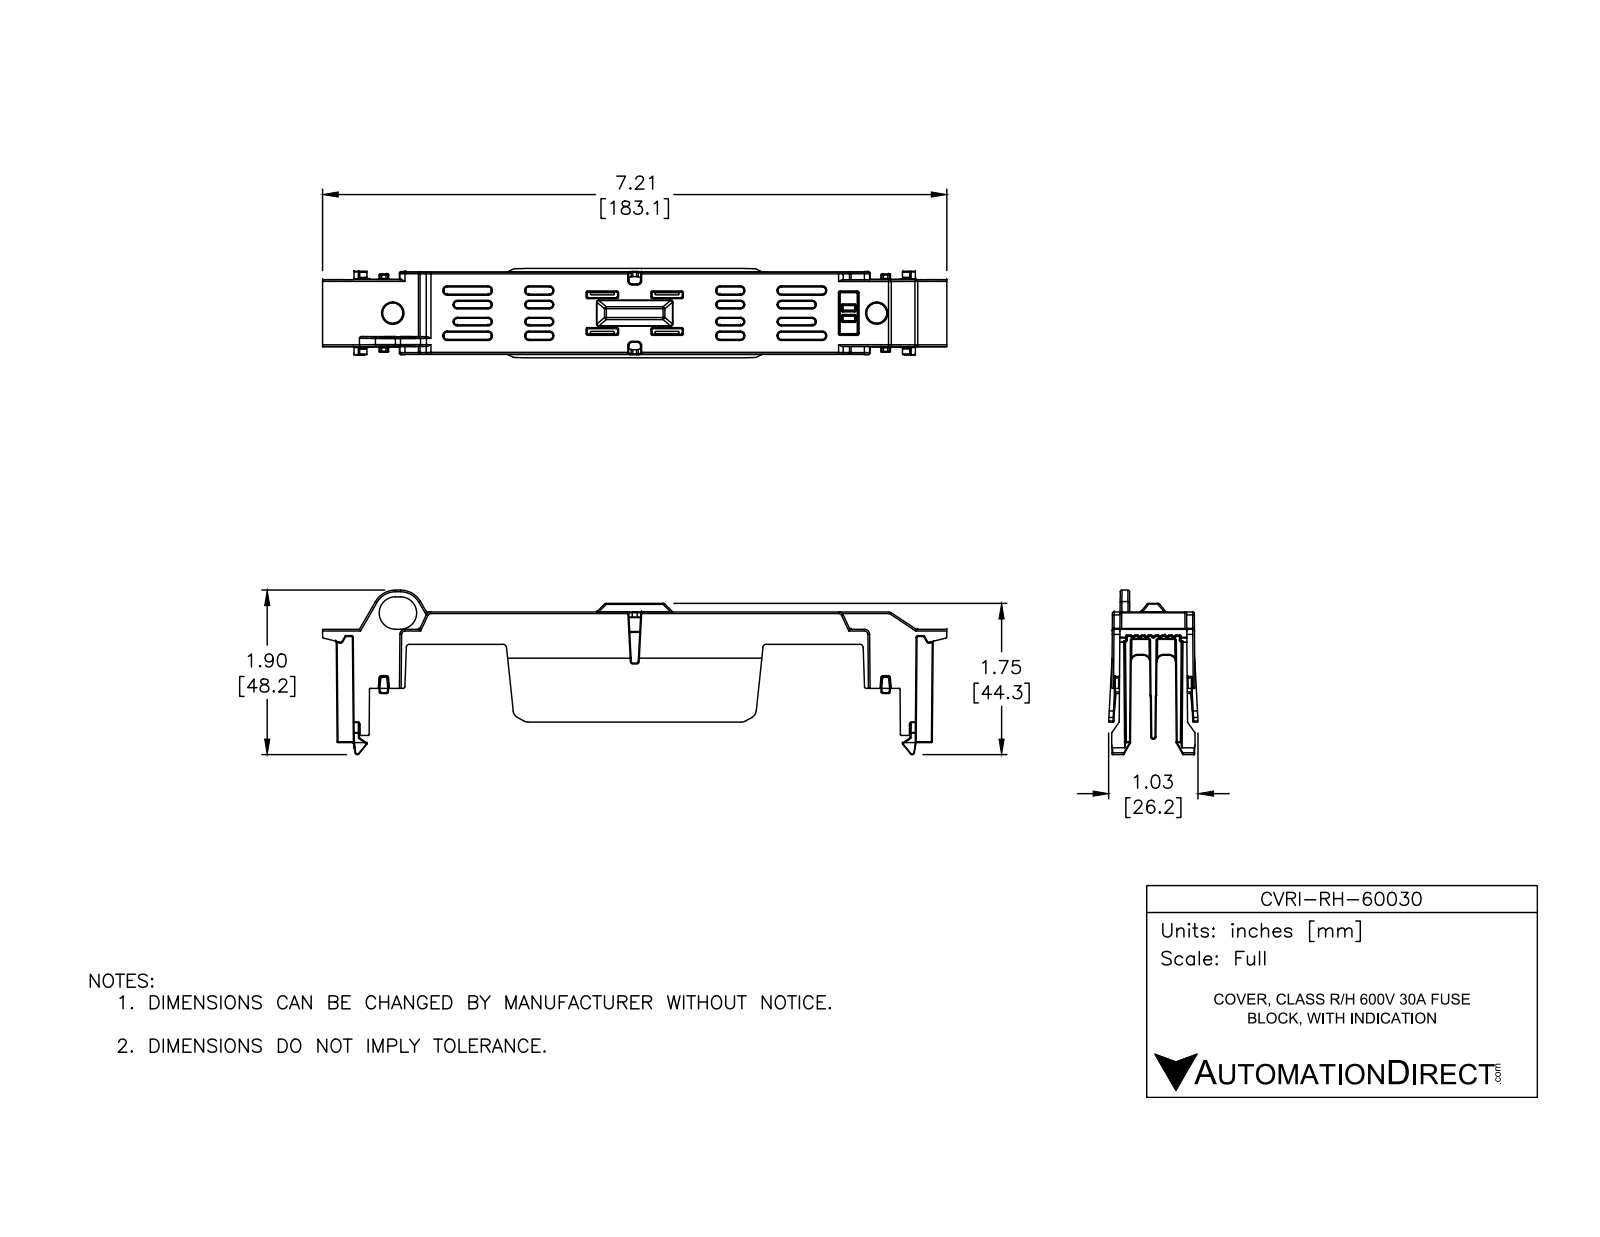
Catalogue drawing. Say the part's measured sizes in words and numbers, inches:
The part is named "CVRI-RH-60030". Its 3-D file was written by "SolidWorks 2016 (AUTOMOTIVE_DESIGN)". It is 1 solid with 2476 faces: 489 planar, 1119 cylindrical and 868 other. Overall it measures 7.207 by 1.899 by 1.032 inches. Its volume is 1.261 cubic inches and its surface area 44.08 square inches. Partial cylindrical surfaces (rounded edges, fillets, slot ends): 417 of radius 0.01, 175 of radius 0.006, 81 of radius 0.039, 52 of radius 0.02, 24 of radius 0.008, 9 of radius 0.03, 6 of radius 0.004, 6 of radius 0.059. The main face-to-face distances are 0.059, 0.089, 0.059, 0.029, 0.148, 0.201, 0.073, 0.132, 0.161, 0.221.
